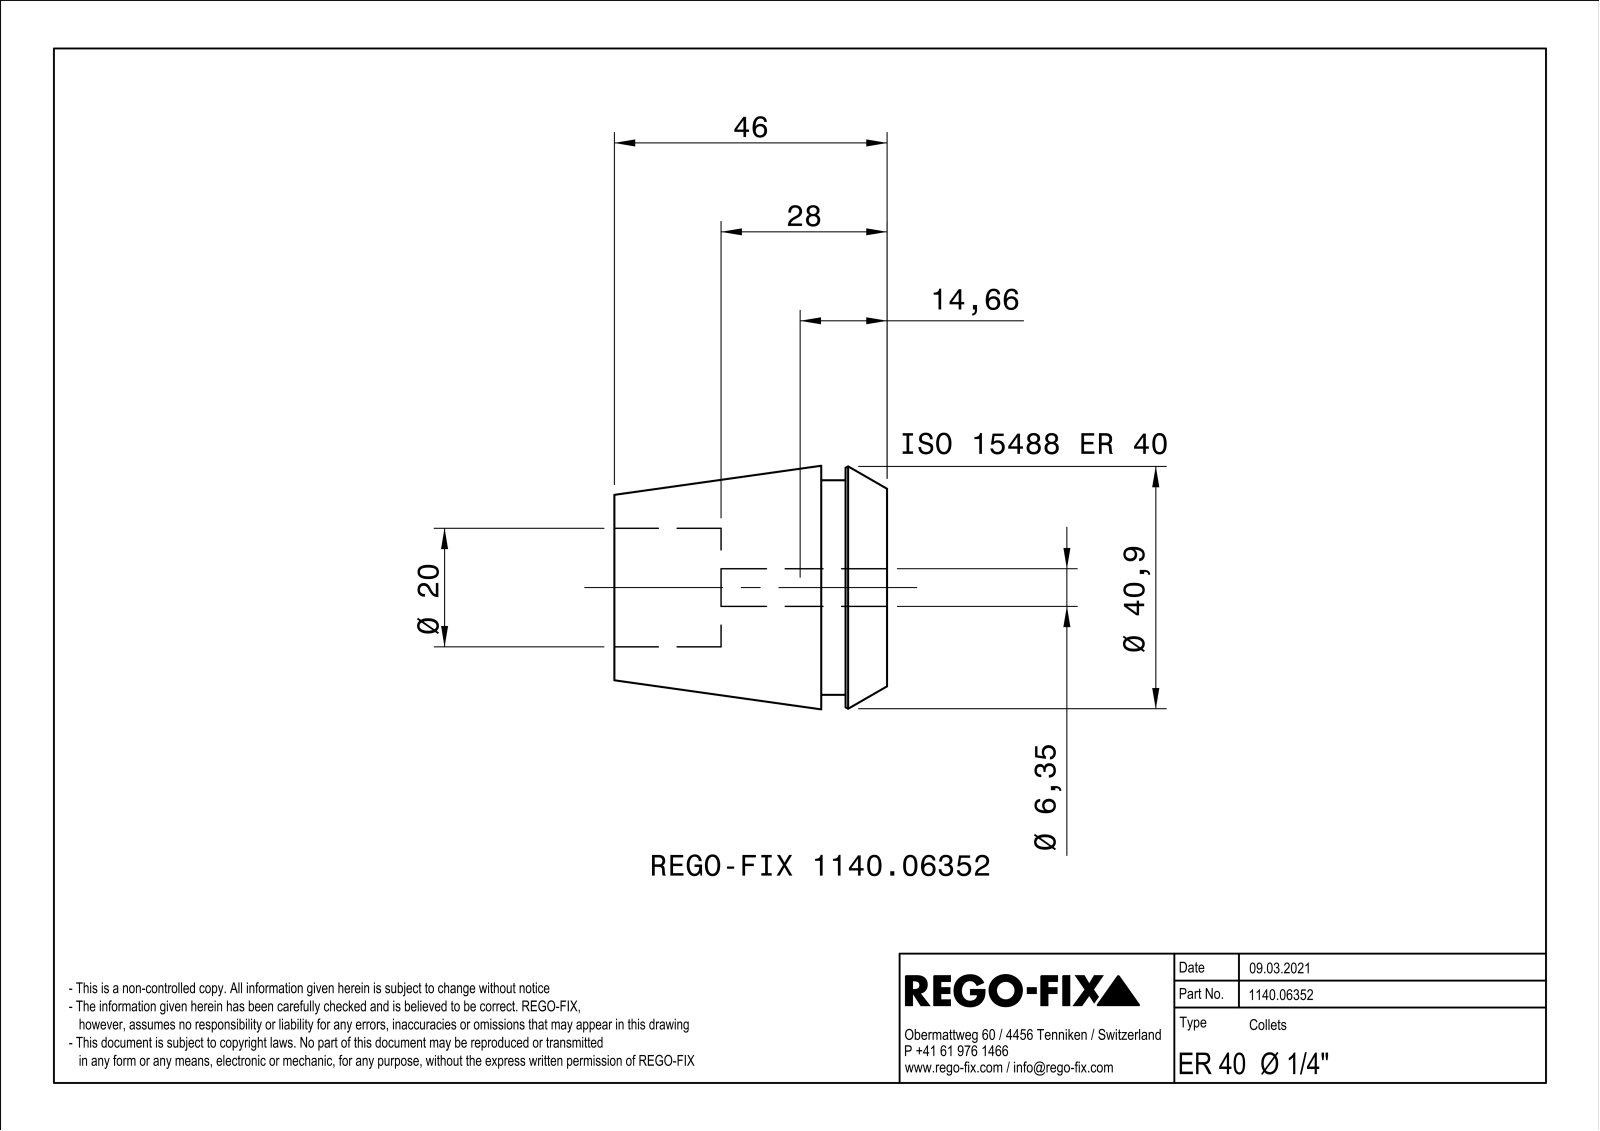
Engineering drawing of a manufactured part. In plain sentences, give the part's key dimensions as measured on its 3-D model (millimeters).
The part is named "NOCUT". Its 3-D file was written by "SIEMENS PLM Software Solid Edge ST10 (AUTOMOTIVE_DESIGN)". It is 1 solid with 272 faces: 104 planar, 48 cylindrical and 120 other. Overall it measures 46 by 40.99 by 40.99 millimeters. Its volume is 36 032 cubic millimeters and its surface area 21 309 square millimeters. Round holes: 1 of diameter 20. Round bosses or shafts: 1 of diameter 36.2. Partial cylindrical surfaces (rounded edges, fillets, slot ends): 8 of radius 45, 1 of radius 3.17. The main face-to-face distances are 0.8, 0.78, 0.82, 46, 11.1, 34.9, 7, 4.1, 39, 28.
